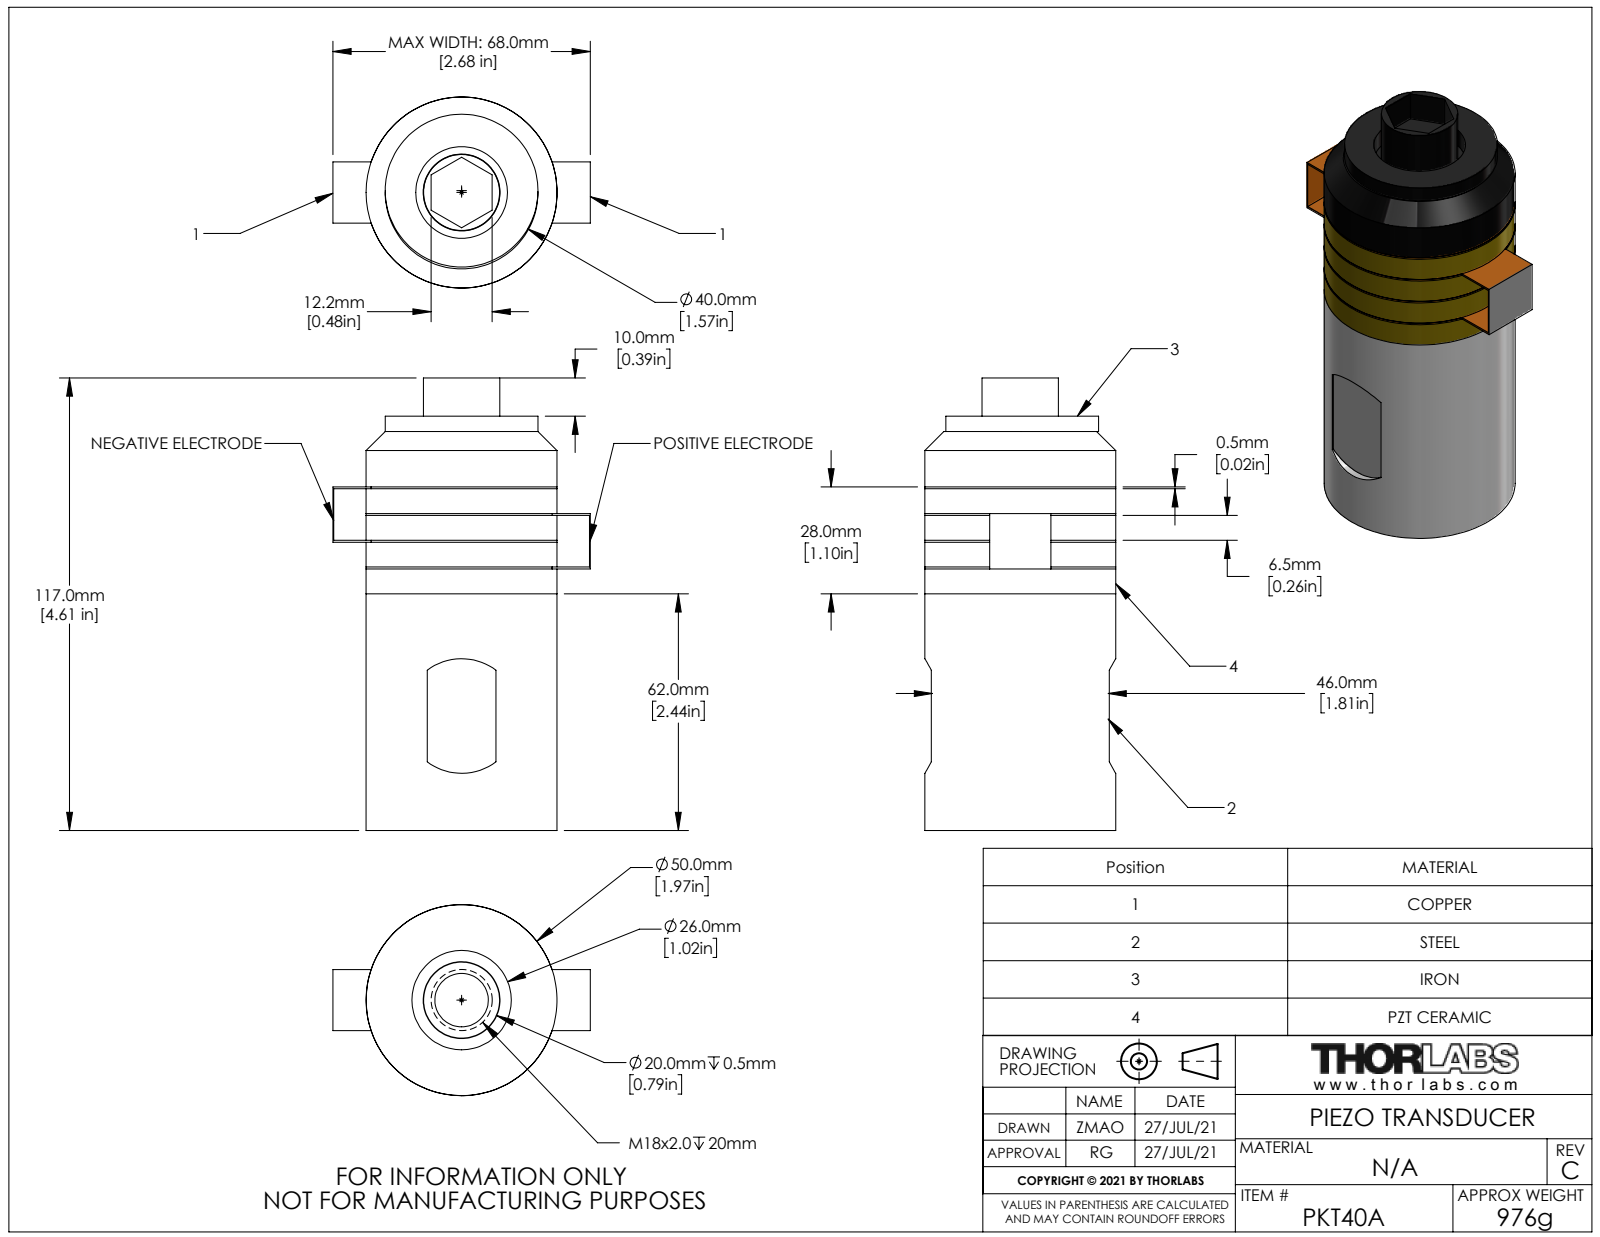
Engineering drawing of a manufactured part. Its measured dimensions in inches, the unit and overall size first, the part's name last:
Units: inches
Overall size (bounding box): 4.665 × 2.653 × 1.969
Round holes (diameter × count): ⌀0.551 ×1, ⌀0.945 ×1, ⌀1.024 ×1
Round bosses / shafts (diameter × count): ⌀1.969 ×1, ⌀1.969 ×1, ⌀1.575 ×1, ⌀0.787 ×1
Partial cylindrical surfaces — rounded edges, fillets, slot ends (radius × count): R0.591 ×1
Main face-to-face distances: 0.276, 0.02, 4.272, 0.551, 0.827, 1.811, 0.295, 2.645, 0.256, 0.807
Volume: 12.3 in³ · Surface area: 40.43 in²
Bodies: 1 solid, 78 faces (36 planar, 38 cylindrical, 4 other)
Part name (STEP PRODUCT): CTN016251-E0W
STEP written by: SolidWorks 2018 (AUTOMOTIVE_DESIGN)
